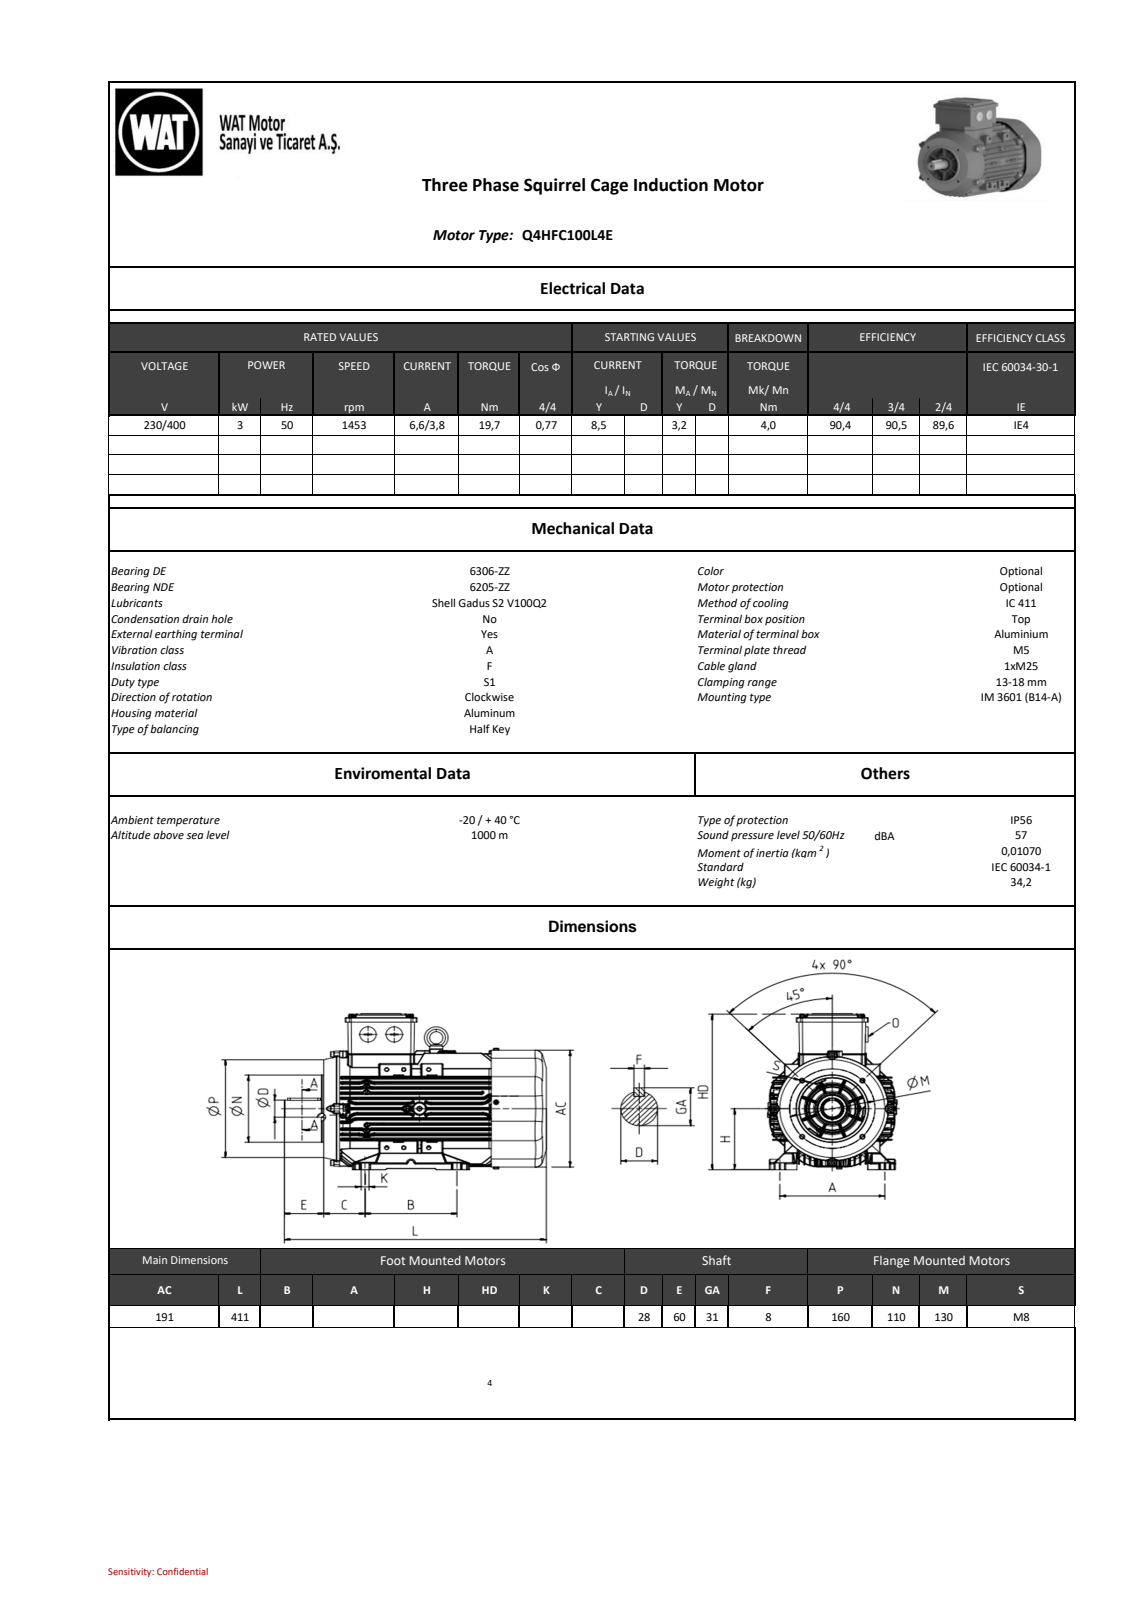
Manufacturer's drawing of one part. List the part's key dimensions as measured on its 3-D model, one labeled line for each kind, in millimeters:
Part name (STEP PRODUCT): QH100 B35 KTA-M2_stp_objects
STEP written by: SIEMENS PLM Software NX2206.8101 (AUTOMOTIVE_DESIGN)
Units: millimetres
Bodies: 0 solids, 5074 faces (1091 planar, 1918 cylindrical, 2065 other)
Overall size (bounding box): 411.25 × 241.35 × 197.57
Round holes (diameter × count): ⌀6.8 ×4, ⌀10 ×1, ⌀10.5 ×1, ⌀12 ×1, ⌀43.9 ×1, ⌀44.1 ×1, ⌀52 ×1, ⌀57.4 ×1, ⌀89 ×1, ⌀129 ×1
Round bosses / shafts (diameter × count): ⌀8 ×8, ⌀113.5 ×1, ⌀110 ×1, ⌀93.5 ×1, ⌀61 ×1, ⌀30 ×1, ⌀29 ×1, ⌀28 ×1
Partial cylindrical surfaces — rounded edges, fillets, slot ends (radius × count): R0.8 ×564, R1 ×460, R2 ×79, R0.81 ×51, R0.5 ×36, R5 ×36, R15 ×26, R4.5 ×16
Main face-to-face distances: 8.53, 8.46, 8.45, 76.24, 16.91, 93.45, 25.58, 17.05, 76.68, 59.63
Hole centre spacings: 65, 91.92, 129.99
